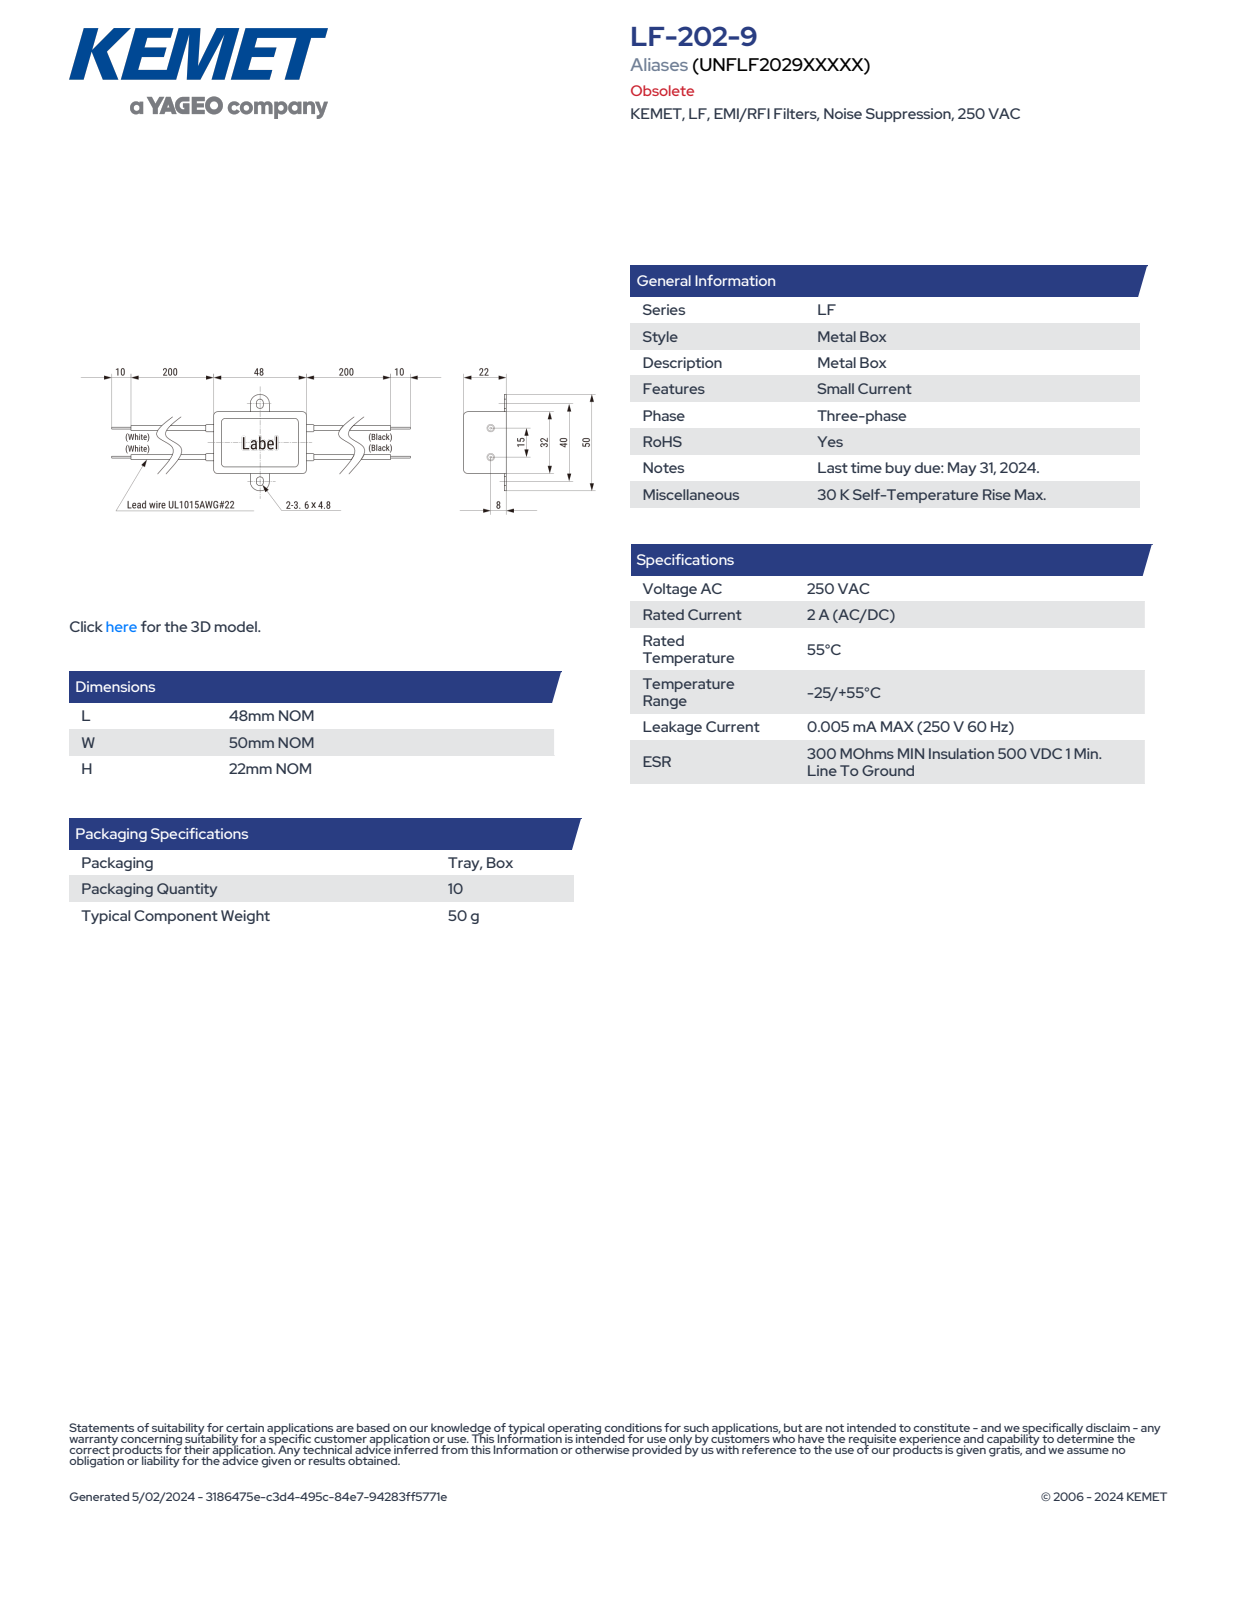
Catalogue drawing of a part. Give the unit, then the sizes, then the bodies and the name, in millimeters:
Units: millimetres
Overall size (bounding box): 468 × 50 × 22
Round bosses / shafts (diameter × count): ⌀2.49 ×2, ⌀1 ×2, ⌀0.8 ×2
Partial cylindrical surfaces — rounded edges, fillets, slot ends (radius × count): R4 ×8, R1 ×4, R1.8 ×4, R4.75 ×2
Main face-to-face distances: 22, 32, 48, 1, 21, 3, 51, 22.25, 31.75, 19.25
Volume: 33 800 mm³ · Surface area: 9 108 mm²
Bodies: 1 solid, 131 faces (82 planar, 45 cylindrical, 4 other)
Part name (STEP PRODUCT): ENF_KLF2029_L48W50H22
STEP written by: SolidWorks 2014 (AUTOMOTIVE_DESIGN)
